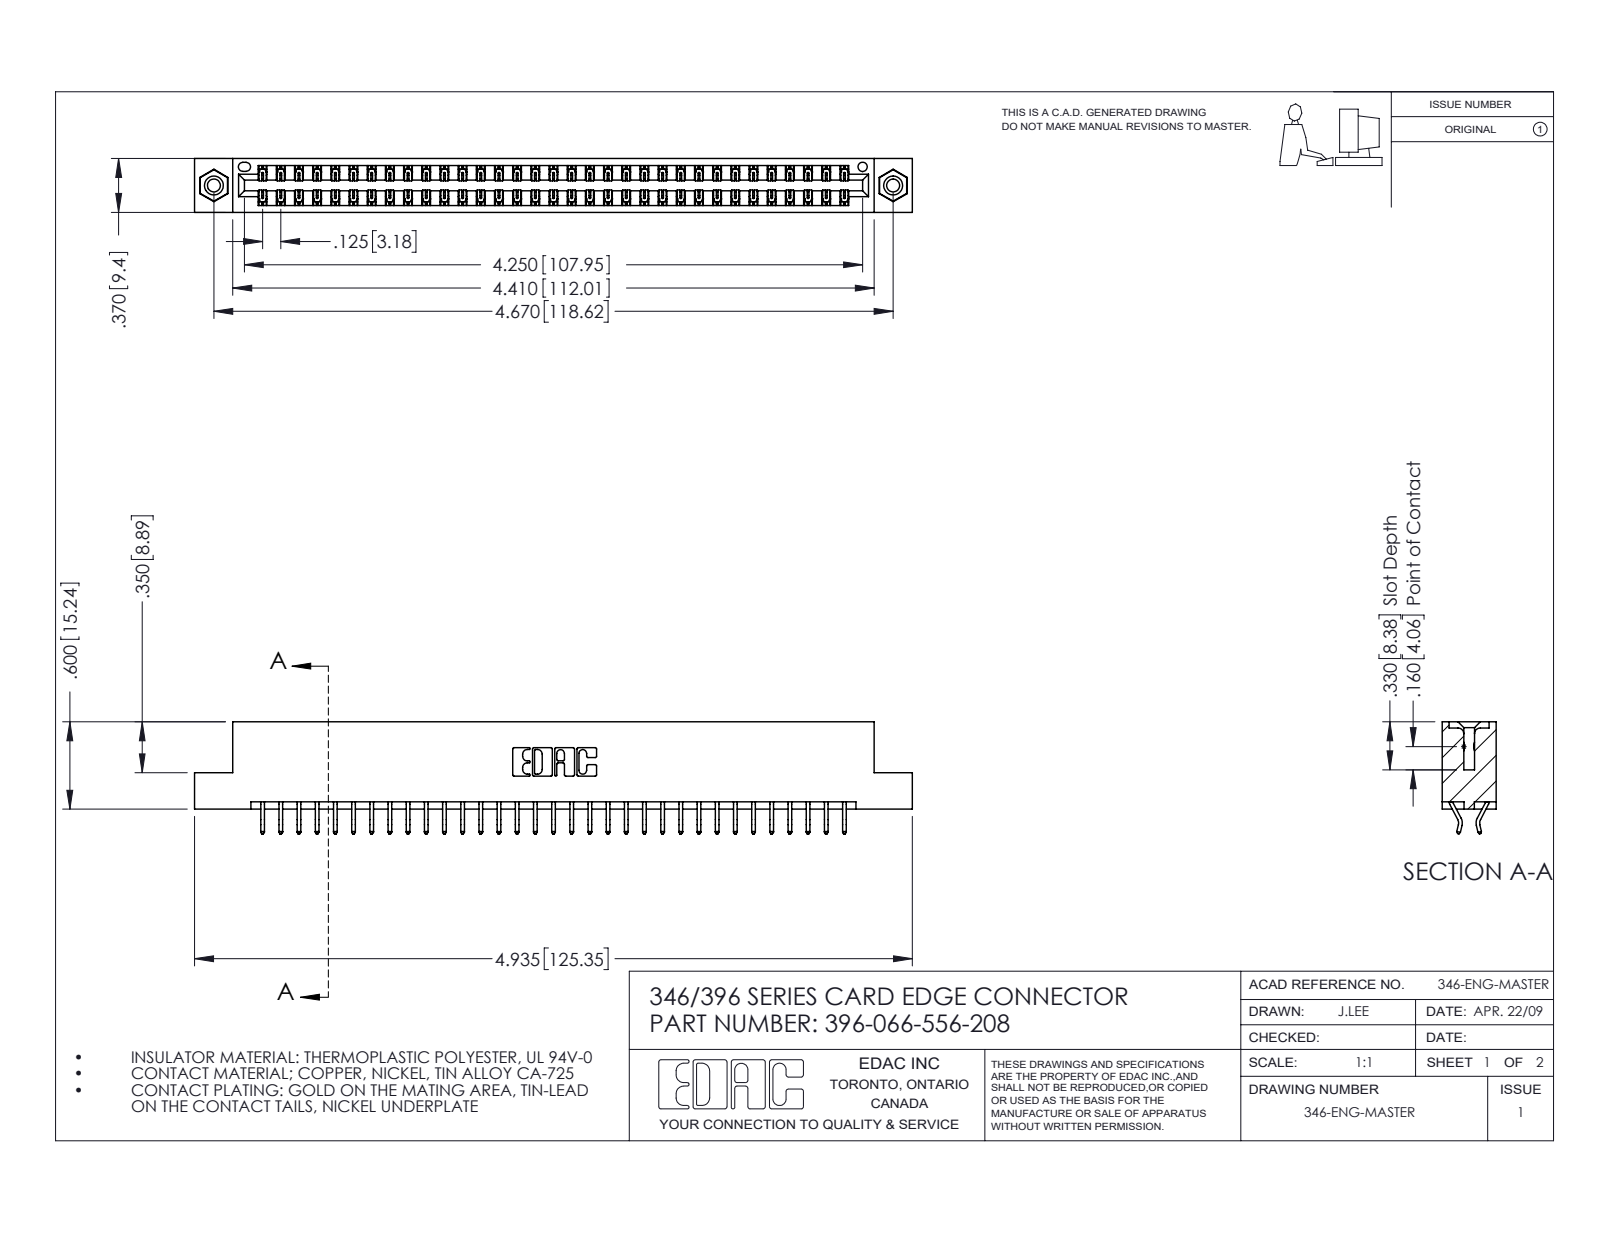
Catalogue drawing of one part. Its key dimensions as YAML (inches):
part_name: "396-066-556-208; 345-250-001_345-250-003-102; 345-292-001_556 Tail; 346 Part_Flush Mounting Lugs - 0.156 Dia-TI"
step_written_by: "SolidWorks 2016 (CONFIG_CONTROL_DESIGN)"
units: inches
bodies: {solids: 69, faces: 4010, planar: 2682, cylindrical: 1312, other: 16}
overall_size: [4.935, 0.77, 0.37]
volume: 0.741
surface_area: 25.59
round_holes:
  - {diameter: 0.089, count: 2}
  - {diameter: 0.125, count: 2}
  - {diameter: 0.156, count: 2}
  - {diameter: 0.064, count: 1}
round_bosses_or_shafts:
  - {diameter: 0.155, count: 2}
partial_cylinders:
  - {radius: 0.006, count: 99}
  - {radius: 0.01, count: 22}
  - {radius: 0.007, count: 6}
  - {radius: 0.031, count: 6}
  - {radius: 0.026, count: 3}
  - {radius: 0.01, count: 2}
  - {radius: 0.014, count: 2}
  - {radius: 0.022, count: 2}
face_to_face_distances: [0.048, 0.322, 0.37, 0.25, 0.025, 0.072, 0.298, 0.275, 0.148, 0.222]
hole_center_spacings: [0.246, 4.462, 4.67]
